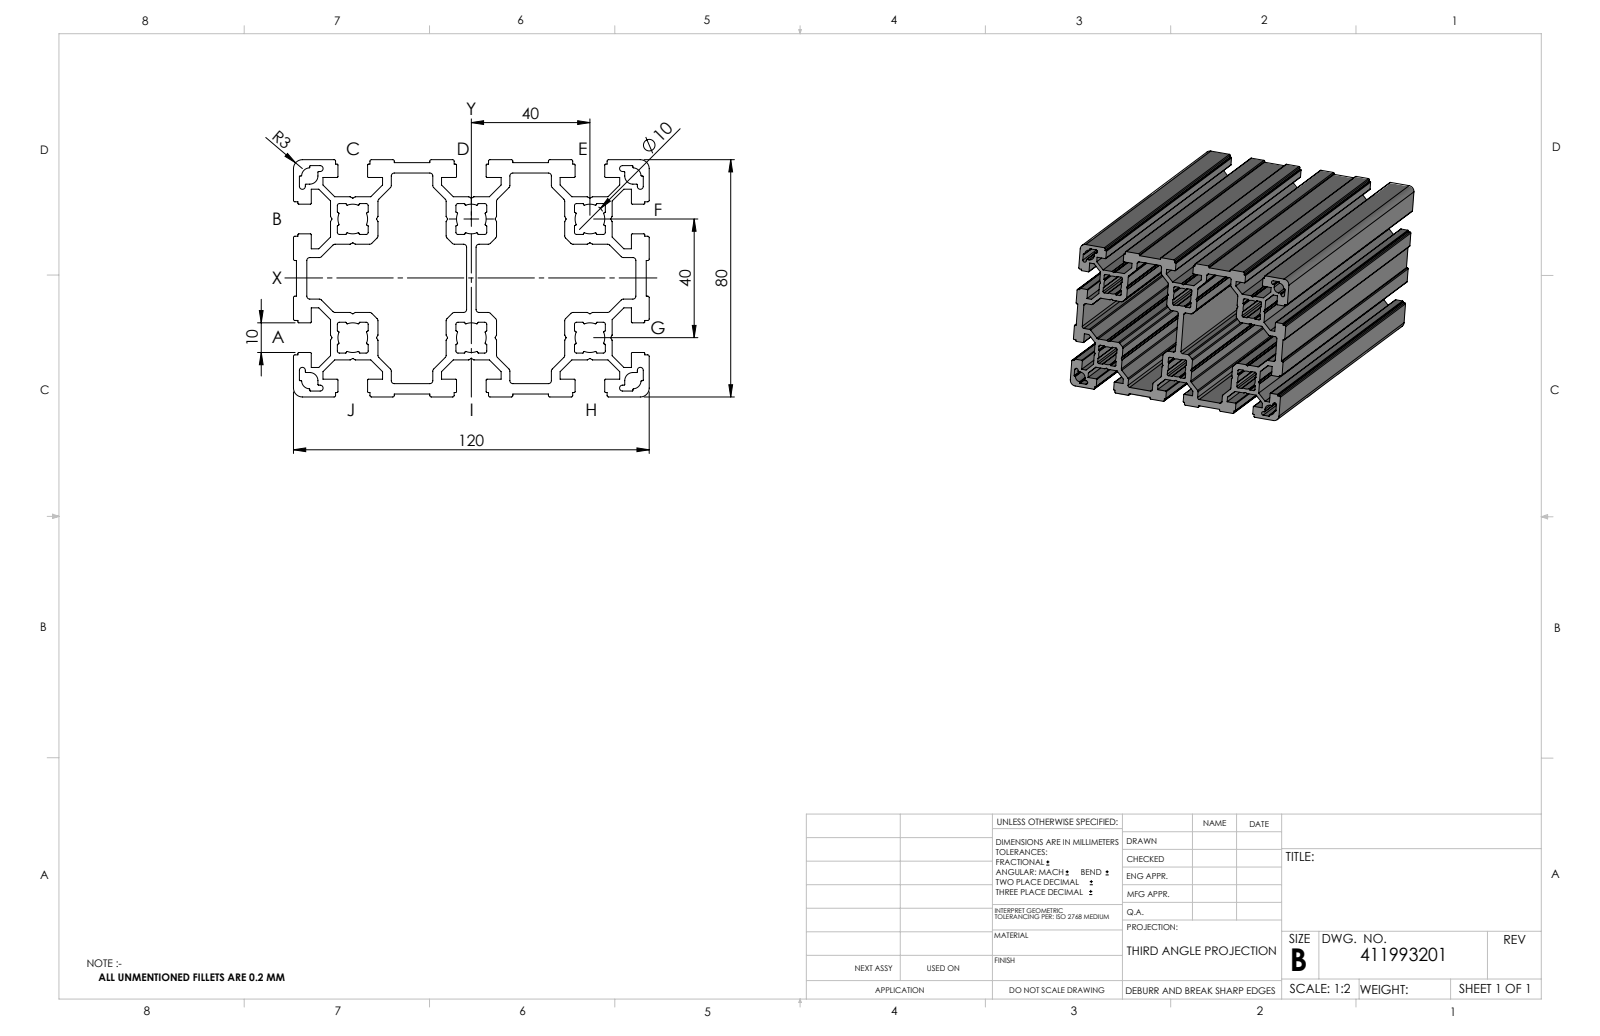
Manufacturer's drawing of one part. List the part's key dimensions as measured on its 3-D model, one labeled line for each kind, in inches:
Part name (STEP PRODUCT): 411993201_c_1
STEP written by: SolidWorks 2014 (CONFIG_CONTROL_DESIGN)
Units: inches
Bodies: 1 solid, 827 faces (420 planar, 407 cylindrical, 0 other)
Overall size (bounding box): 7.874 × 4.724 × 3.15
Volume: 32.21 in³ · Surface area: 511.2 in²
Partial cylindrical surfaces — rounded edges, fillets, slot ends (radius × count): R0.008 ×186, R0.039 ×64, R0.012 ×40, R0.02 ×32, R0.028 ×24, R0.197 ×6, R0.108 ×4, R0.118 ×4
Main face-to-face distances: 0.492, 1.575, 0.63, 1.113, 0.236, 0.256, 1.122, 2.028, 1.535, 0.886
